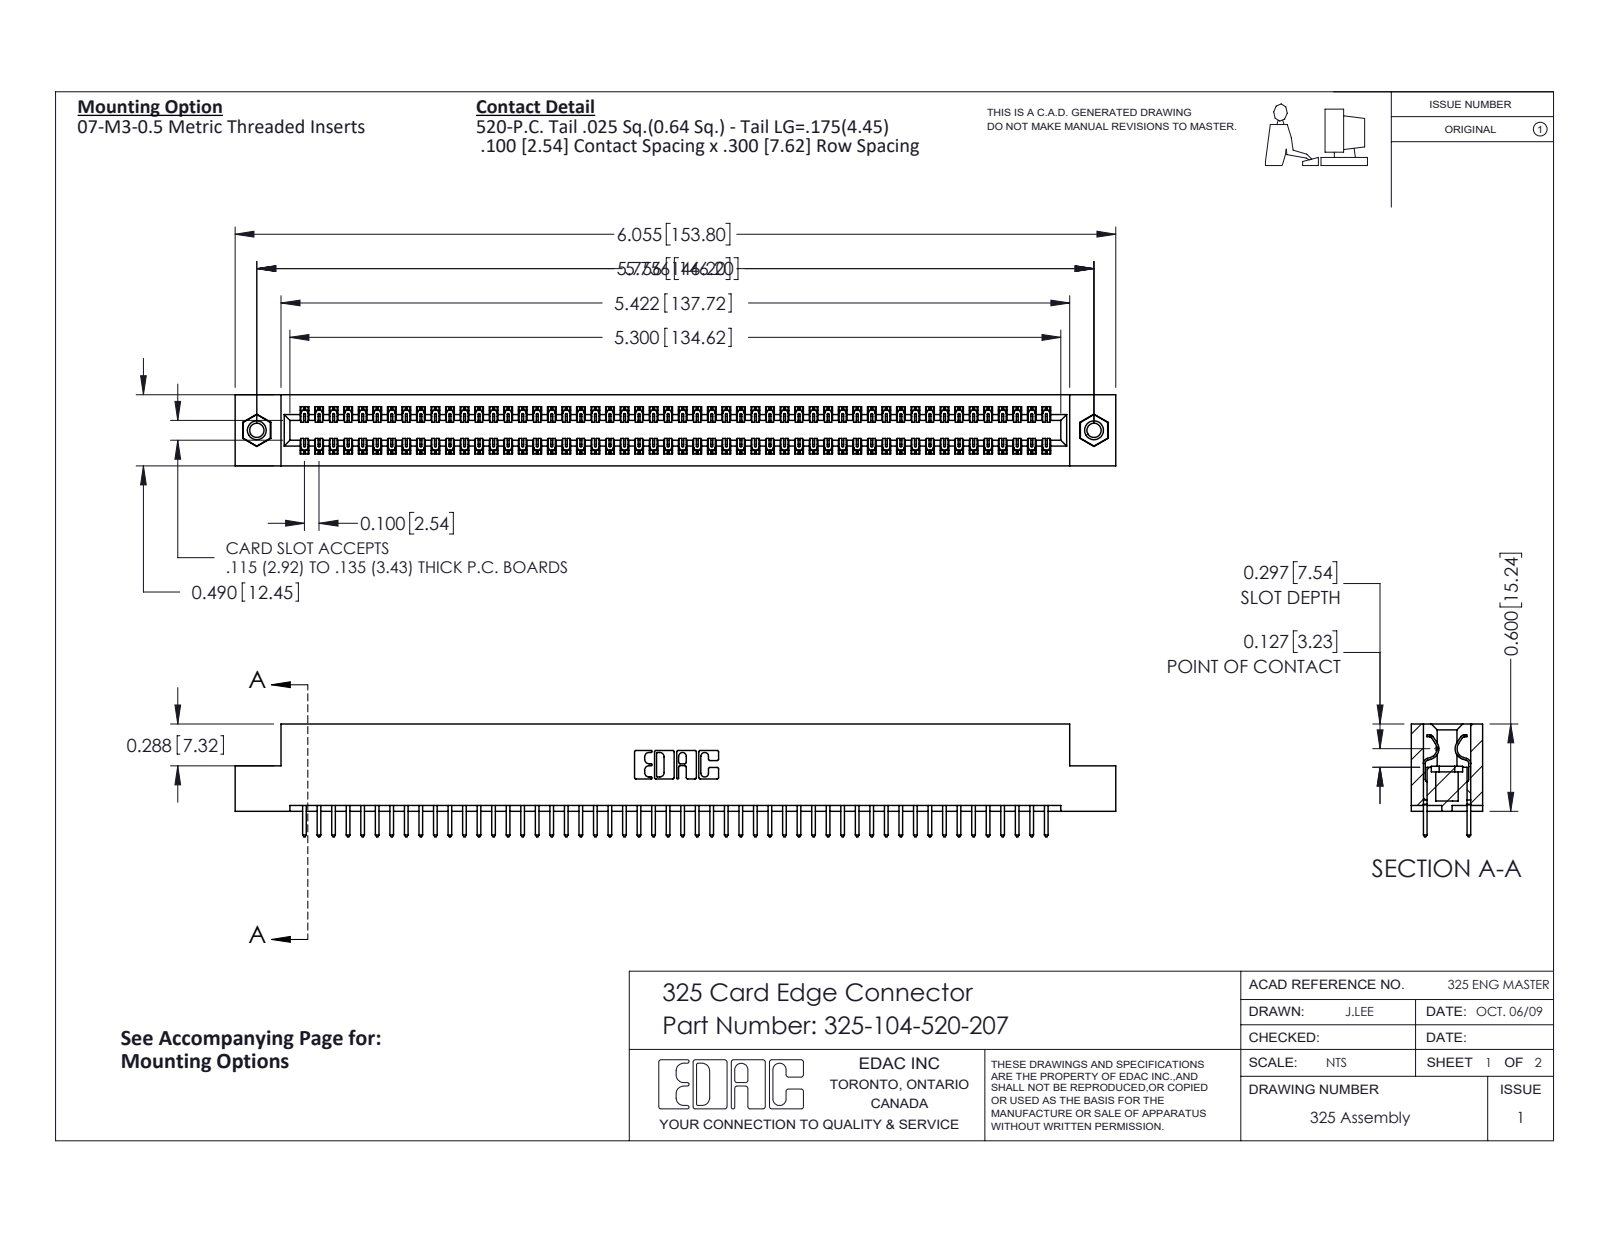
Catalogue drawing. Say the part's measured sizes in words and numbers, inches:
The part is named "325-104-520-207; 325-292-001_325-293-120; 345-250-001_345-250-005-103; 325 Part_TI". Its 3-D file was written by "SolidWorks 2016 (CONFIG_CONTROL_DESIGN)". It is 107 solids with 5582 faces: 3846 planar, 1720 cylindrical and 16 other. Overall it measures 6.055 by 0.775 by 0.49 inches. Its volume is 1.215 cubic inches and its surface area 37.44 square inches. Round holes: 2 of diameter 0.098, 2 of diameter 0.125, 2 of diameter 0.16. Round bosses or shafts: 2 of diameter 0.155. Partial cylindrical surfaces (rounded edges, fillets, slot ends): 156 of radius 0.006, 104 of radius 0.01, 22 of radius 0.01, 6 of radius 0.007, 6 of radius 0.031, 3 of radius 0.026, 2 of radius 0.014, 2 of radius 0.022. The main face-to-face distances are 0.083, 0.407, 0.3, 0.49, 0.107, 0.383, 0.025, 0.325, 0.275, 0.56. The hole center spacings are 5.756.
